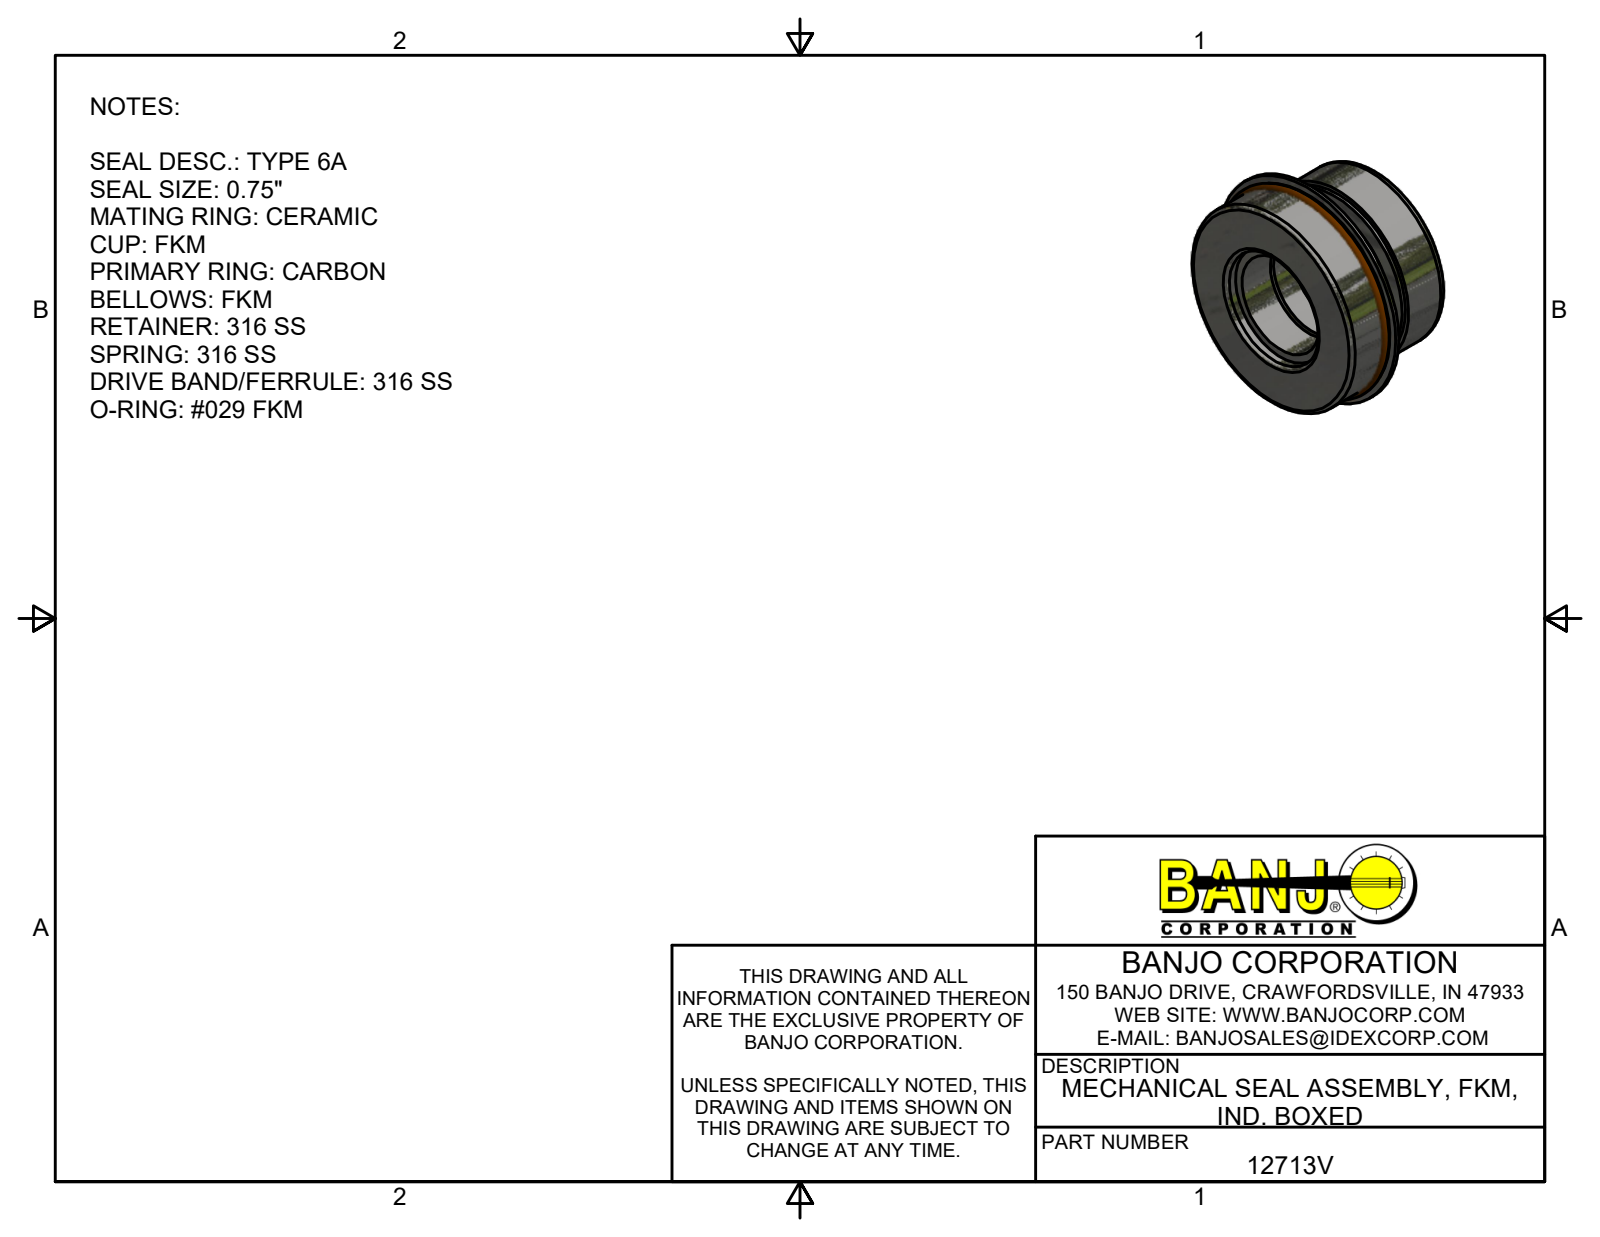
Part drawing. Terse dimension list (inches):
name: 12713V
written by: Autodesk Inventor 2022 (AUTOMOTIVE_DESIGN)
unit: in
bodies: 1 solid, 31 faces (12 planar, 13 cylindrical, 6 other)
size: 1.72 × 1.72 × 1.021
volume: 1.131 in³; area: 11.99 in²
holes: 1× ⌀0.75, 1× ⌀0.813, 1× ⌀0.875, 1× ⌀1
bosses: 1× ⌀1.72, 1× ⌀1.575, 1× ⌀1.375, 1× ⌀1.313, 1× ⌀1.305, 1× ⌀1.125, 1× ⌀1.063
face distances: 0.38, 0.031, 0.615, 0.235, 0.406, 0.375, 1.021, 0.641, 0.99, 0.61
